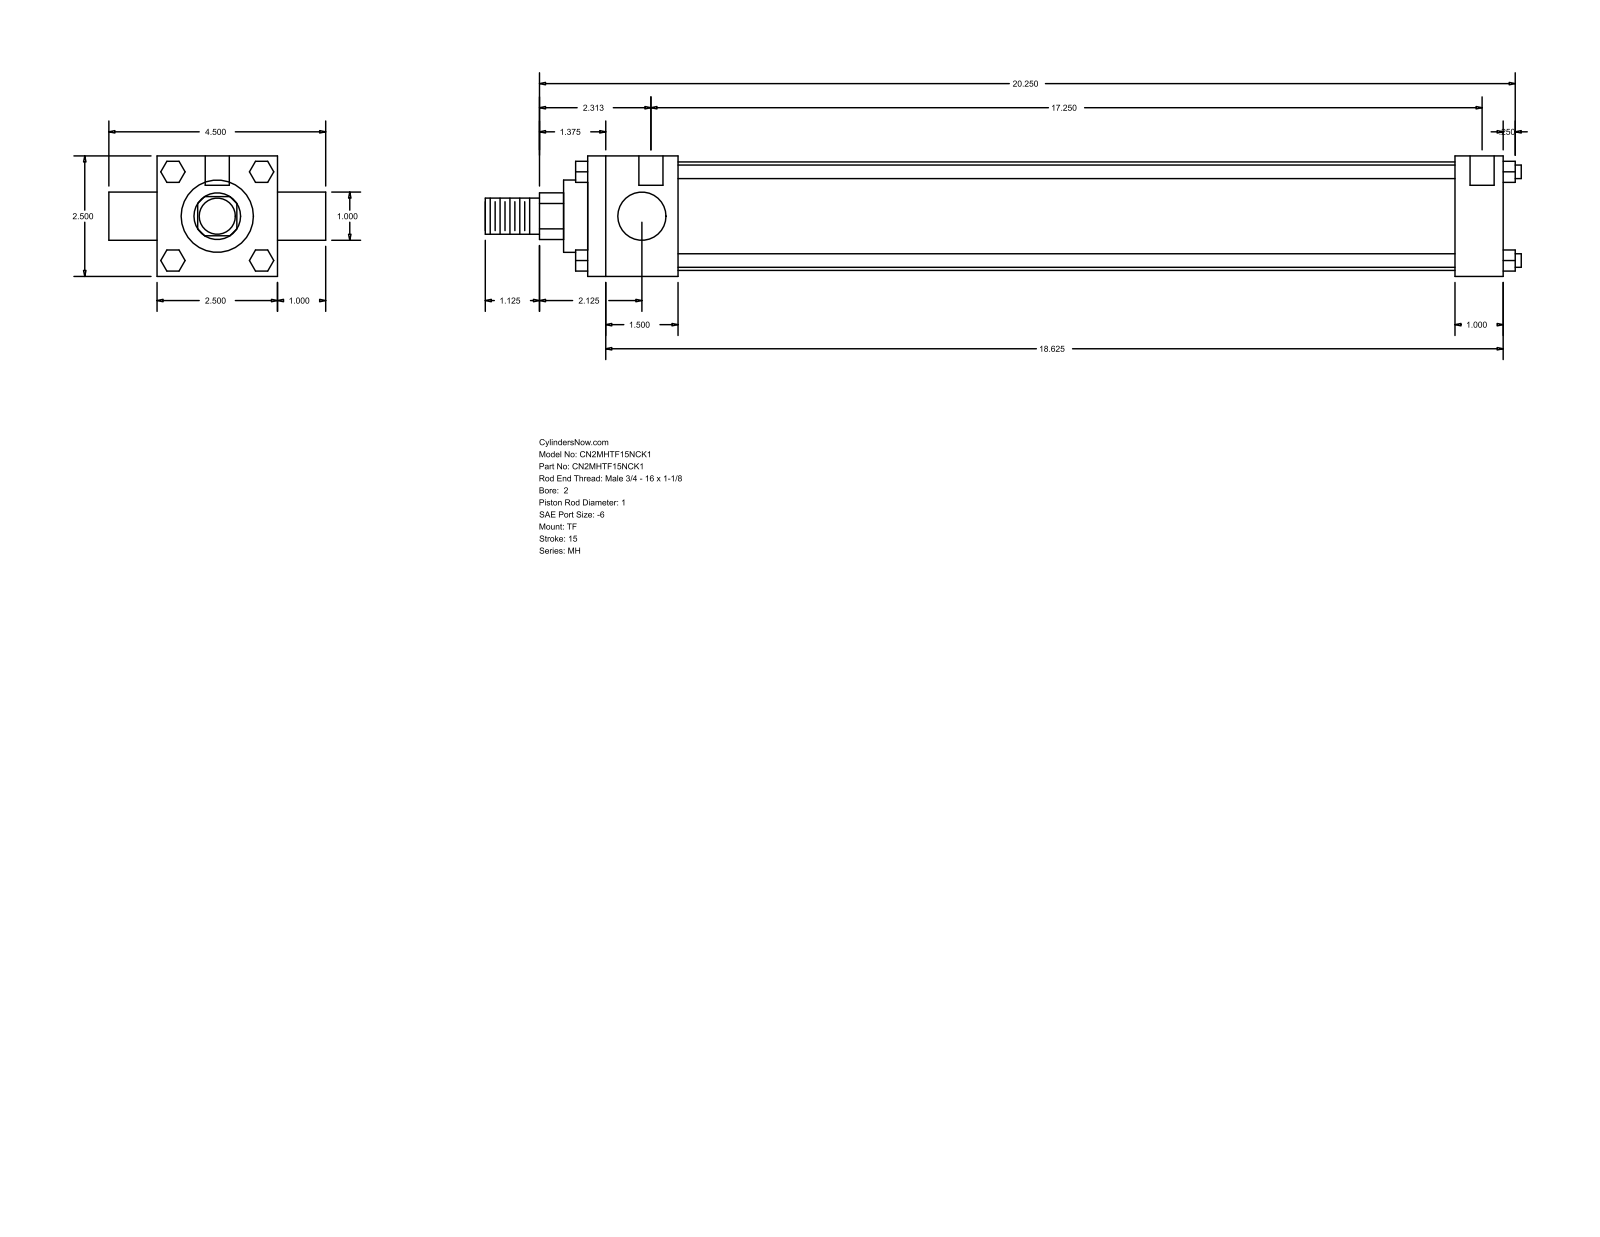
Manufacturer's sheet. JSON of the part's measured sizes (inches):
{"part_name": "MH_TF__0200_1", "step_written_by": "GSSL Pune (CONFIG_CONTROL_DESIGN)", "units": "inches", "bodies": {"solids": 0, "faces": 120, "planar": 92, "cylindrical": 28, "other": 0}, "overall_size": [21.5, 4.5, 2.5], "round_holes": [[0.219, 3], [0.5, 2]], "round_bosses_or_shafts": [[0.281, 4], [1, 2], [2.25, 1], [1.5, 1], [0.75, 1]], "partial_cylinders_radius": [[0.484, 1]], "face_to_face_distances": [2.5, 19, 1, 1.875, 18, 16.125, 17.125, 3.5, 19.5, 0.25], "hole_center_spacings": [0.125, 0.187, 17.25, 17.375, 17.437, 17.562]}
